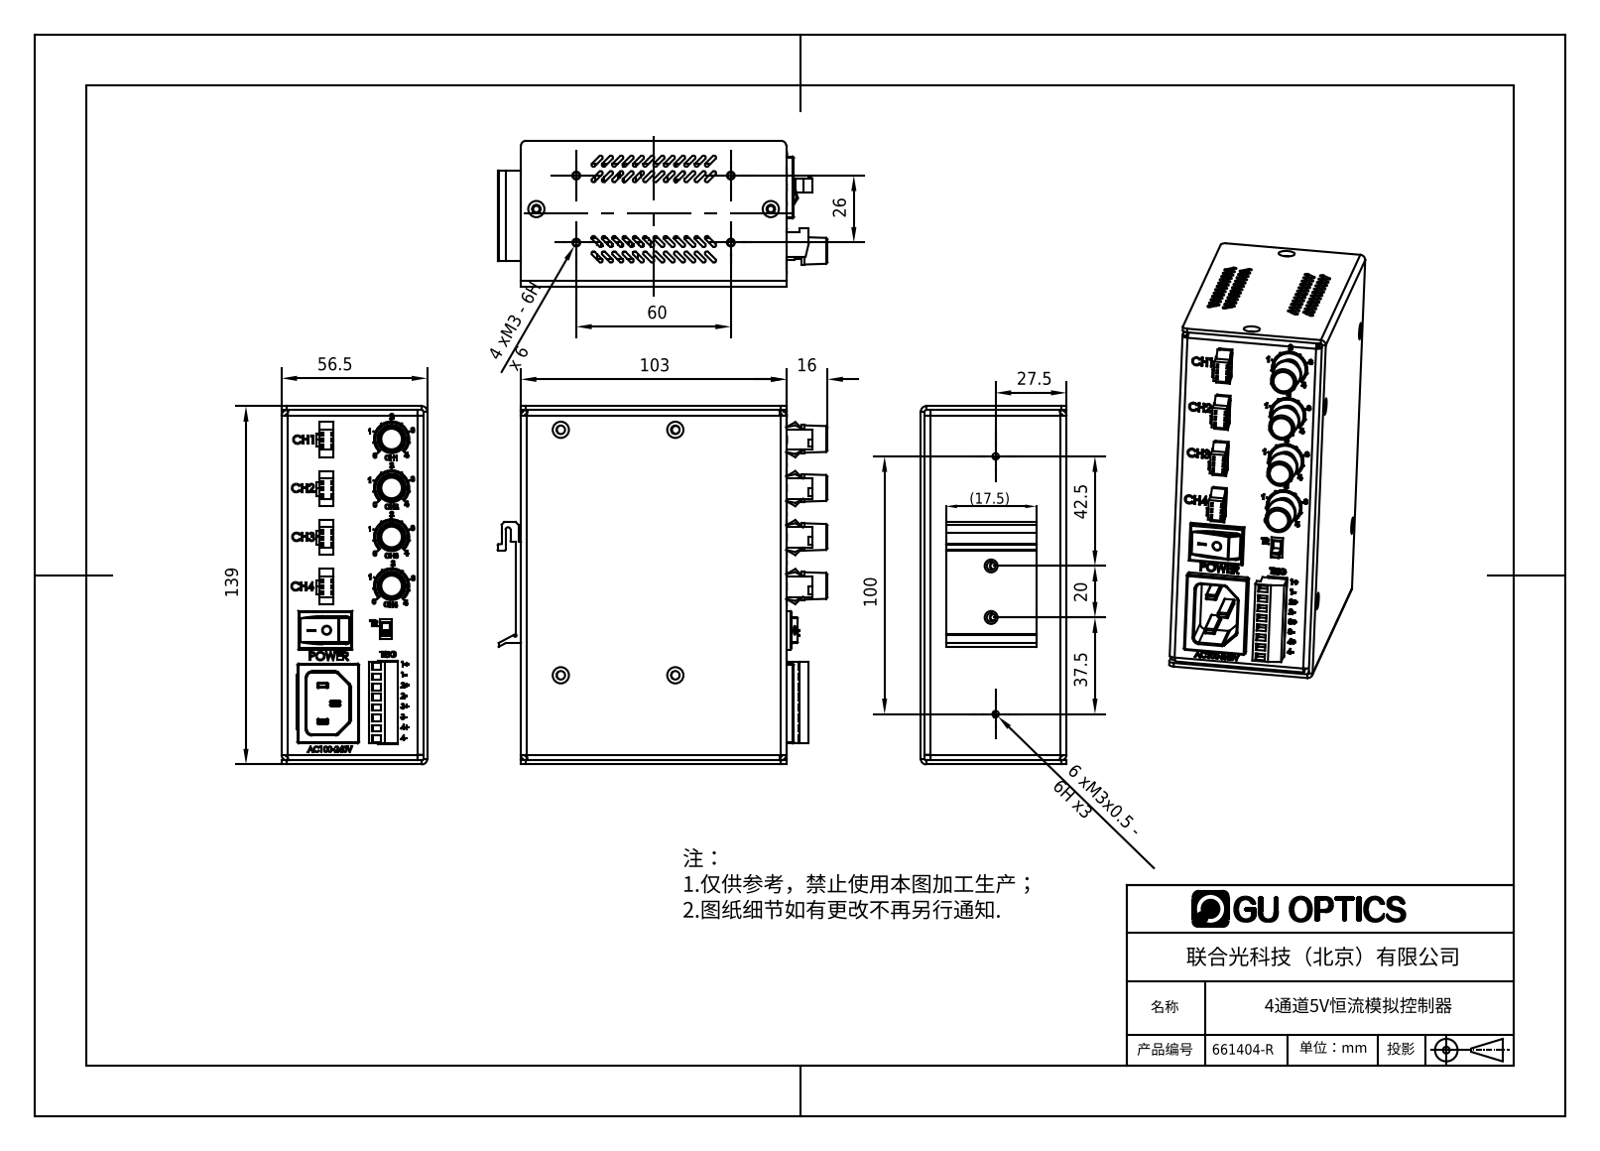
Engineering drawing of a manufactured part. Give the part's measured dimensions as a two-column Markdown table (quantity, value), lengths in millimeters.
| quantity | value |
| --- | --- |
| part name | 661404 |
| STEP written by | SolidWorks 2016 (AUTOMOTIVE_DESIGN) |
| units | millimeters |
| bodies | 116 solids, 3662 faces (2288 planar, 836 cylindrical, 538 other) |
| overall size | 139 × 128 × 56.5 |
| volume | 170 656 mm³ |
| surface area | 184 394 mm² |
| round holes (diameter × count) | 2.5 × 17, 3.5 × 10, 6 × 4, 7.5 × 4, 8 × 4, 2.6 × 2, 3.4 × 2, 5 × 2, 3 × 1 |
| round bosses / shafts (diameter × count) | 11 × 4, 6.8 × 2, 24.14 × 1, 9.31 × 1, 8.28 × 1, 6.71 × 1, 3 × 1 |
| partial cylindrical surfaces (radius × count) | 0.75 × 96, 0.5 × 22, 2 × 17, 0.74 × 10, 2.24 × 10, 1 × 5, 6.3 × 4, 6.5 × 4 |
| main face-to-face distances | 1.5, 55, 53.5, 1.6, 56.5, 101.5, 18.8, 17.3, 36.2, 37.7 |
| hole center spacings | 14.14, 20.23, 76.61, 19, 20, 91, 1, 11 |
